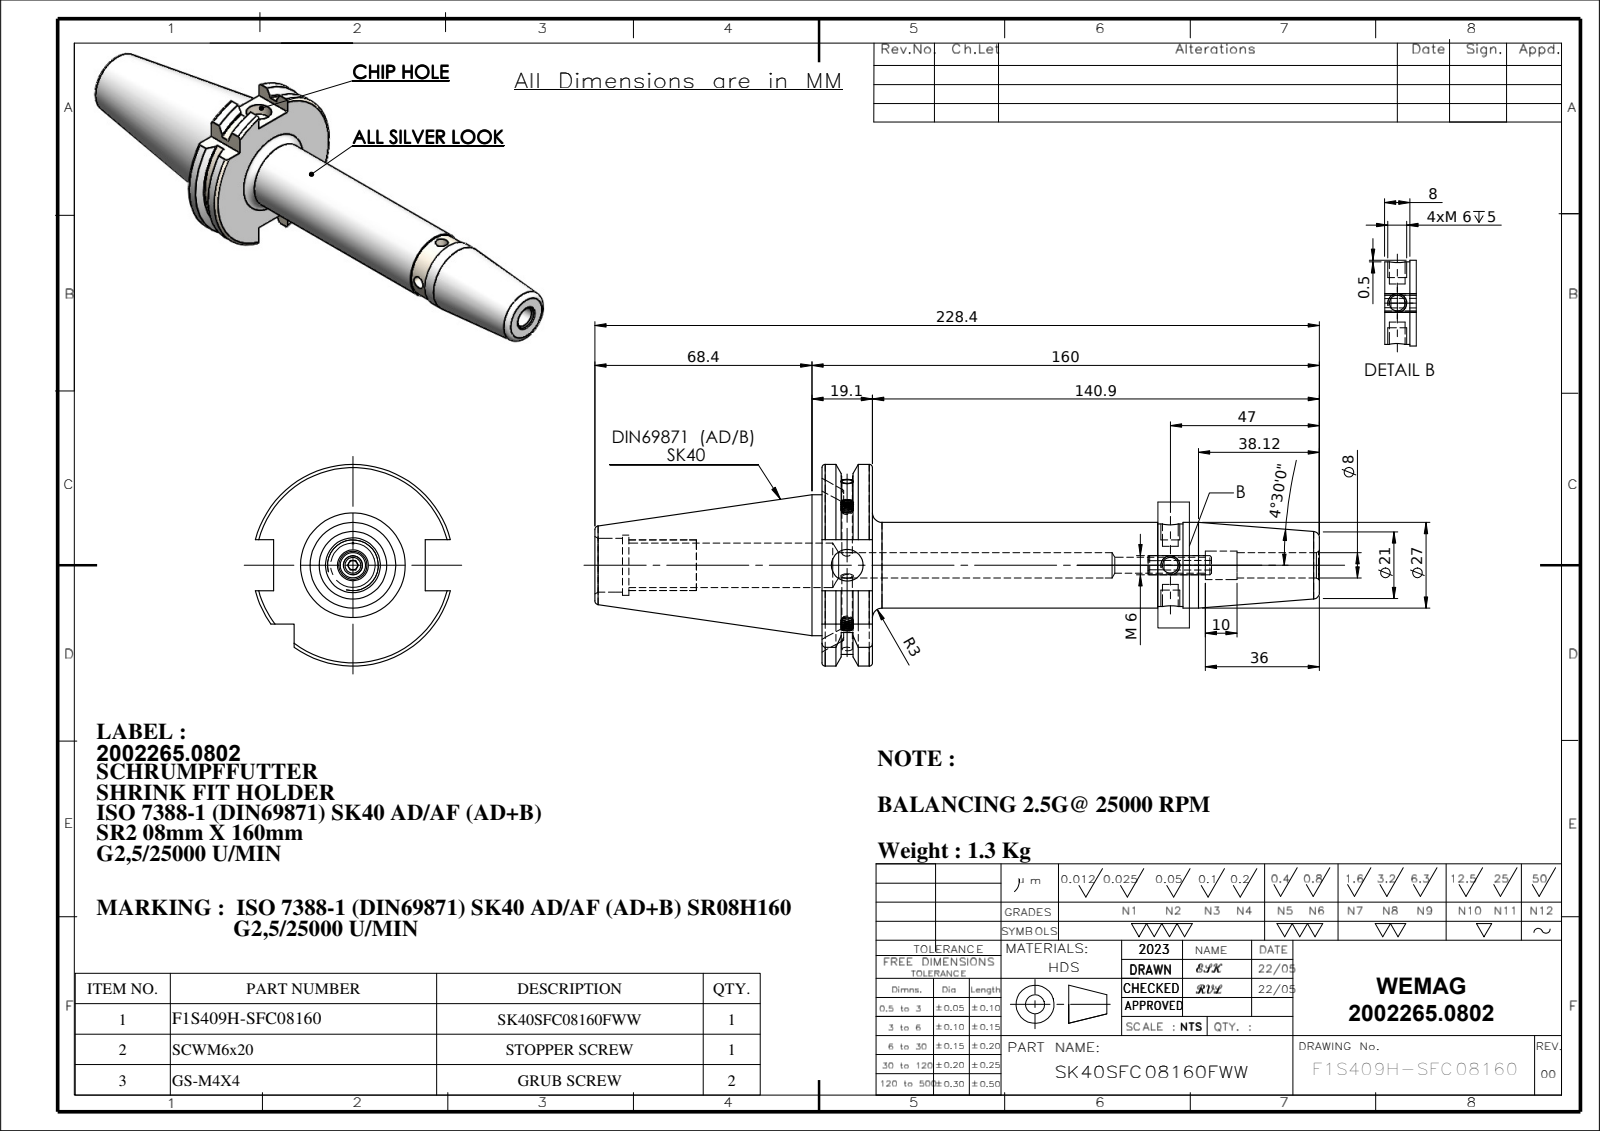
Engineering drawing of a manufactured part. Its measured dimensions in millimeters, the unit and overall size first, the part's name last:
Units: millimetres
Overall size (bounding box): 228.4 × 63.55 × 61.48
Round holes (diameter × count): ⌀5 ×3, ⌀2.9 ×1, ⌀3.3 ×1, ⌀7.99 ×1, ⌀8 ×1, ⌀8.99 ×1, ⌀10 ×1, ⌀14 ×1, ⌀17 ×1, ⌀19 ×1
Round bosses / shafts (diameter × count): ⌀4 ×2, ⌀44.45 ×1, ⌀27 ×1, ⌀26 ×1, ⌀6 ×1
Partial cylindrical surfaces — rounded edges, fillets, slot ends (radius × count): R28.12 ×1, R31.77 ×1
Main face-to-face distances: 15.9, 16.1, 47.8, 156.8, 140.9, 71.6, 87.5, 228.4, 10.7, 60.9
Hole centre spacings: 101.85
Volume: 169 042 mm³ · Surface area: 37 145 mm²
Bodies: 4 solids, 237 faces (63 planar, 72 cylindrical, 102 other)
Part name (STEP PRODUCT): GS-M4X4_DIN 913 - M4 x 4-N; SK40SFC08160FWW; 91406-SR208160; SCWM6
STEP written by: SolidWorks 2018 (CONFIG_CONTROL_DESIGN)
